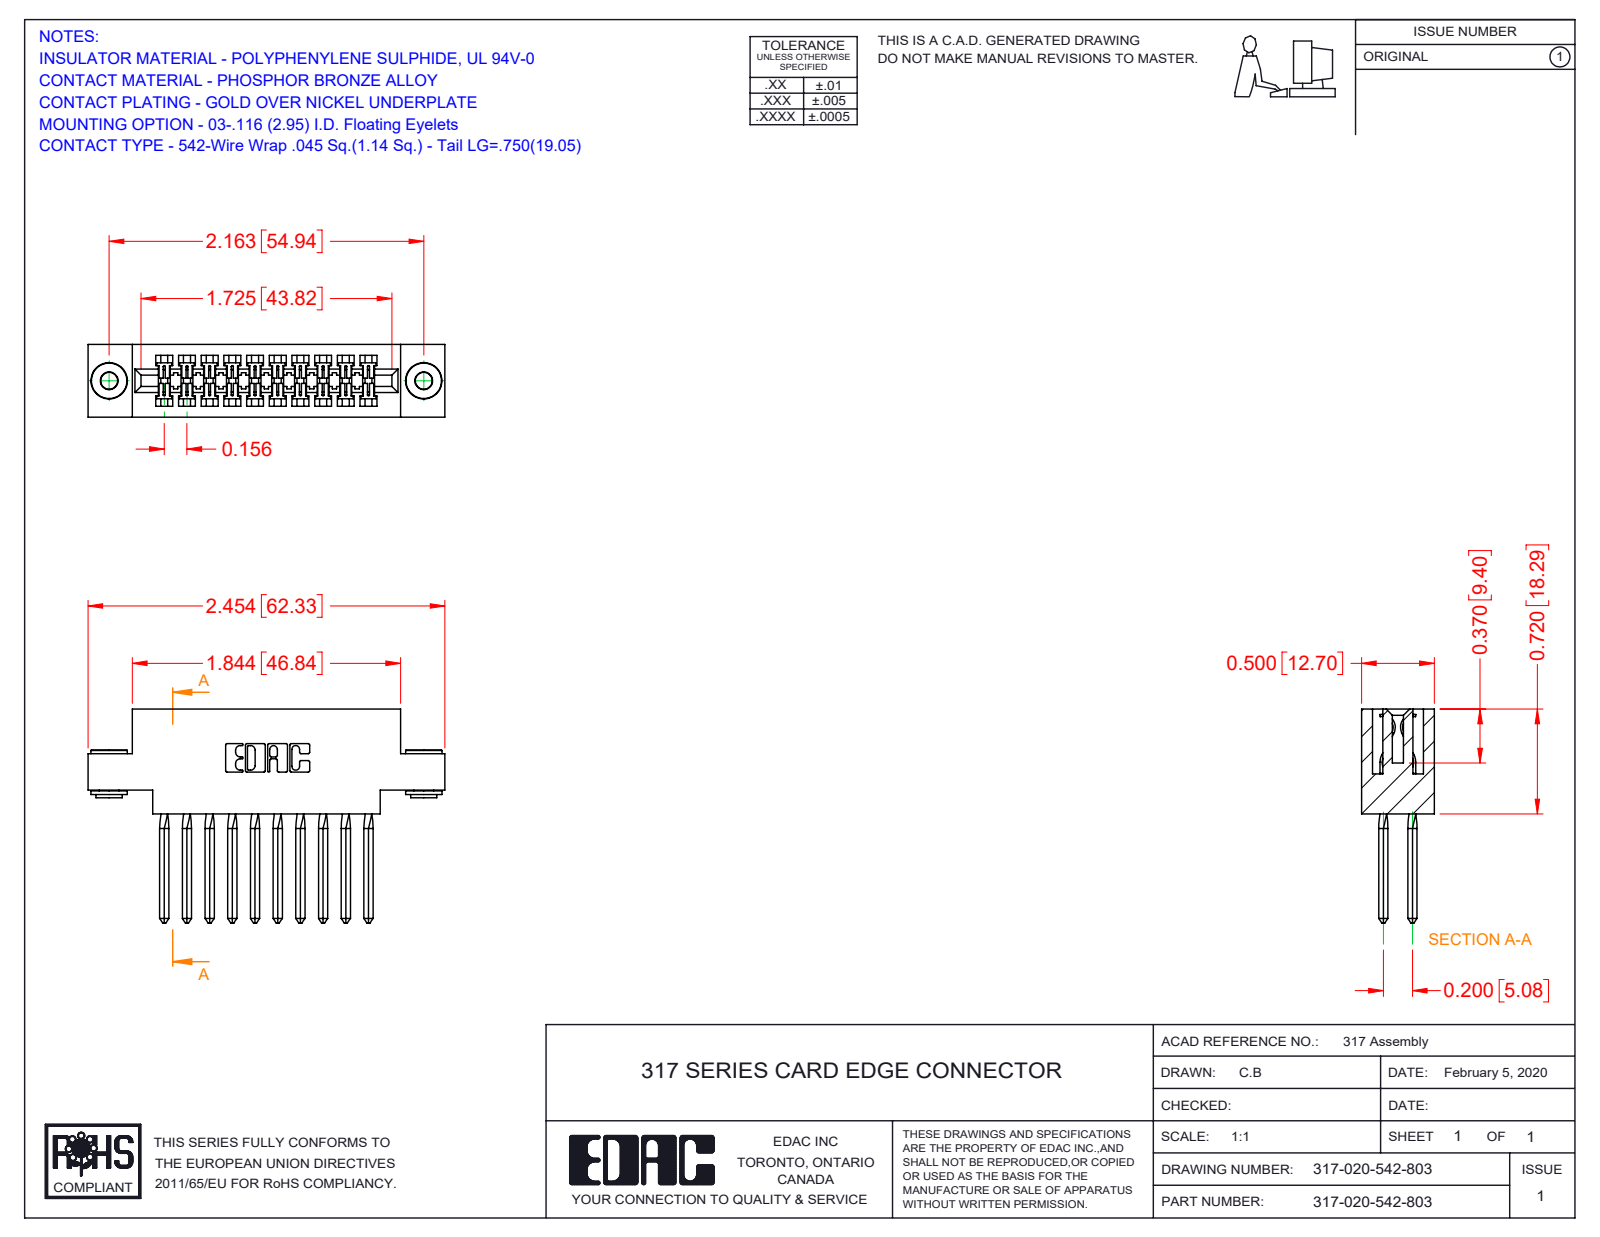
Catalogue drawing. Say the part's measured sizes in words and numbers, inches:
The part is named "317-020-542-803; 317-290-003_542; 345-250-002_345-250-002-102; 317 Part_.156 Dia - TH". Its 3-D file was written by "SolidWorks 2016 (CONFIG_CONTROL_DESIGN)". It is 23 solids with 1280 faces: 988 planar, 204 cylindrical and 88 other. Overall it measures 2.454 by 1.47 by 0.5 inches. Its volume is 0.562 cubic inches and its surface area 18.61 square inches. Round holes: 2 of diameter 0.116, 2 of diameter 0.156. Round bosses or shafts: 2 of diameter 0.25, 2 of diameter 0.18, 2 of diameter 0.136. Partial cylindrical surfaces (rounded edges, fillets, slot ends): 40 of radius 0.006, 22 of radius 0.01, 6 of radius 0.007, 6 of radius 0.031, 3 of radius 0.026, 2 of radius 0.074, 2 of radius 0.089, 2 of radius 0.1. The main face-to-face distances are 0.5, 0.075, 0.425, 0.11, 0.22, 0.116, 0.35, 0.156, 0.2, 0.331. The hole center spacings are 2.163.
